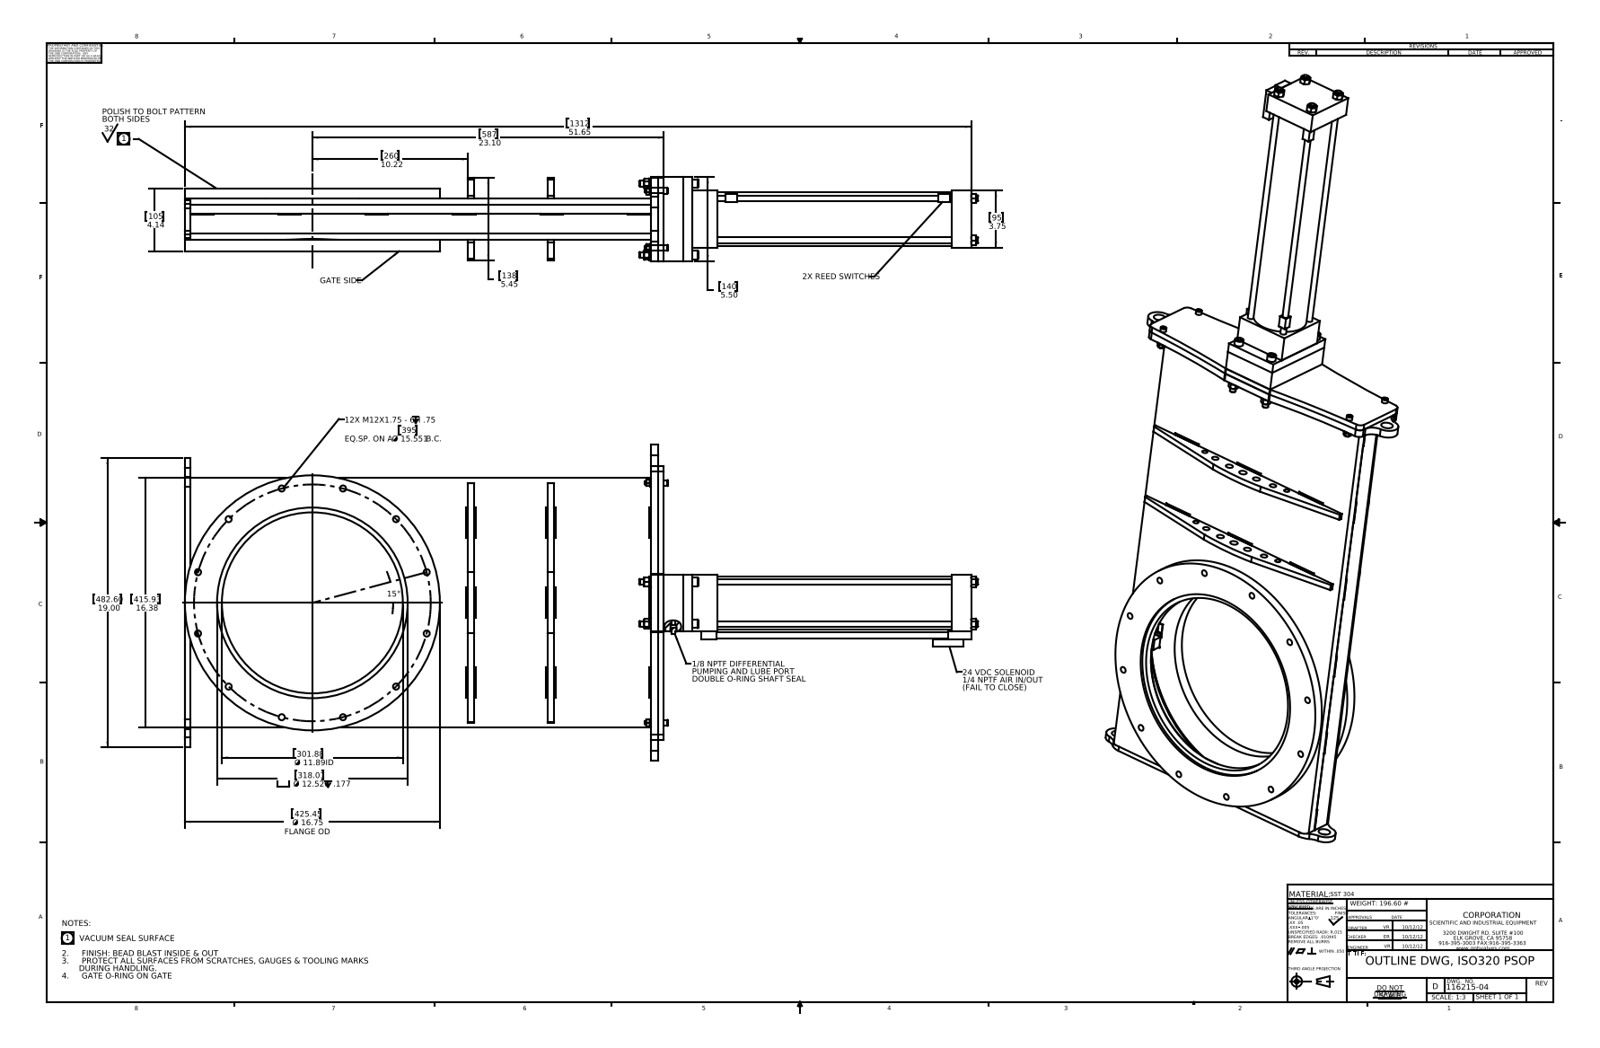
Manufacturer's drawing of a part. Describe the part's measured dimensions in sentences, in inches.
The part is named "116215-04". Its 3-D file was written by "SolidWorks 2014 (CONFIG_CONTROL_DESIGN)". It is 0 solids with 683 faces: 340 planar, 260 cylindrical and 83 other. Overall it measures 52.104 by 20.75 by 5.5 inches. Round holes: 12 of diameter 0.402, 4 of diameter 0.35, 4 of diameter 0.43, 4 of diameter 0.47, 4 of diameter 0.77, 2 of diameter 0.5, 1 of diameter 11.885, 1 of diameter 11.89, 1 of diameter 12.187, 1 of diameter 12.52, 1 of diameter 16. Round bosses or shafts: 8 of diameter 0.375, 4 of diameter 0.683, 4 of diameter 0.563, 4 of diameter 0.487, 4 of diameter 0.375, 4 of diameter 0.25, 1 of diameter 16.75, 1 of diameter 15.99. Partial cylindrical surfaces (rounded edges, fillets, slot ends): 16 of radius 0.375, 8 of radius 0.75, 8 of radius 1, 4 of radius 0.031, 4 of radius 0.2, 4 of radius 0.388, 4 of radius 40, 4 of radius 60. The main face-to-face distances are 0.187, 2.507, 2.32, 2.695, 0.875, 0.375, 16.187, 0.94, 0.687, 3.195. The hole center spacings are 7.776, 15.021, 4.025, 7.775, 10.996, 13.467, 1.036, 1.144.
